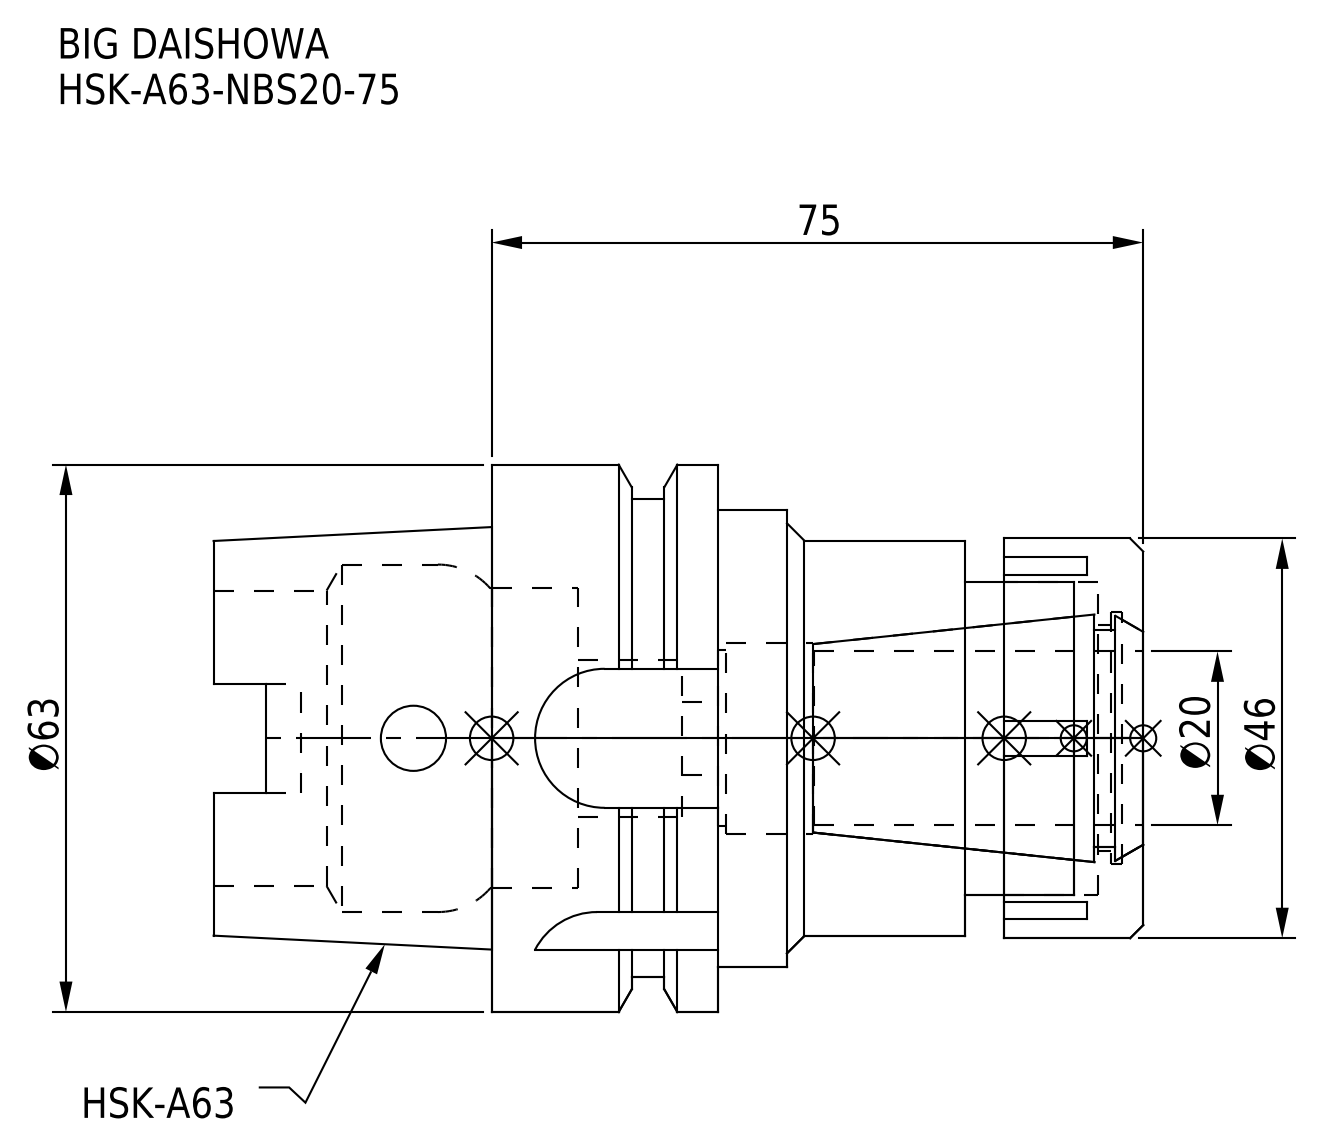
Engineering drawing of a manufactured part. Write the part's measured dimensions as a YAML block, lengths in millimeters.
part_name: "HSK-A63-NBS20-75_1.stp; DXF_TEMP_ASSY_ASM_4_ASM.stp; HA63NB20075-200_ASM.stp; HSK-A63-NBS20-75-FreeParts (+3 more)"
step_written_by: "SolidWorks 2019 (CONFIG_CONTROL_DESIGN)"
units: millimeters
bodies: {solids: 2, faces: 141, planar: 70, cylindrical: 49, other: 22}
overall_size: [107, 63, 63]
volume: 138505
surface_area: 37435
round_holes:
  - {diameter: 7.5, count: 1}
  - {diameter: 8.4, count: 1}
  - {diameter: 18, count: 1}
  - {diameter: 20.3, count: 1}
  - {diameter: 22, count: 1}
  - {diameter: 26, count: 1}
  - {diameter: 29, count: 1}
  - {diameter: 34, count: 1}
  - {diameter: 34.5, count: 1}
  - {diameter: 36, count: 1}
  - {diameter: 40, count: 1}
round_bosses_or_shafts:
  - {diameter: 63, count: 1}
  - {diameter: 55, count: 1}
  - {diameter: 52.6, count: 1}
  - {diameter: 46, count: 1}
  - {diameter: 45.5, count: 1}
partial_cylinders:
  - {radius: 2.88, count: 4}
  - {radius: 8, count: 4}
face_to_face_distances: [26, 8, 49, 75, 20.5, 33, 65.05, 16.05, 9.95, 41]
